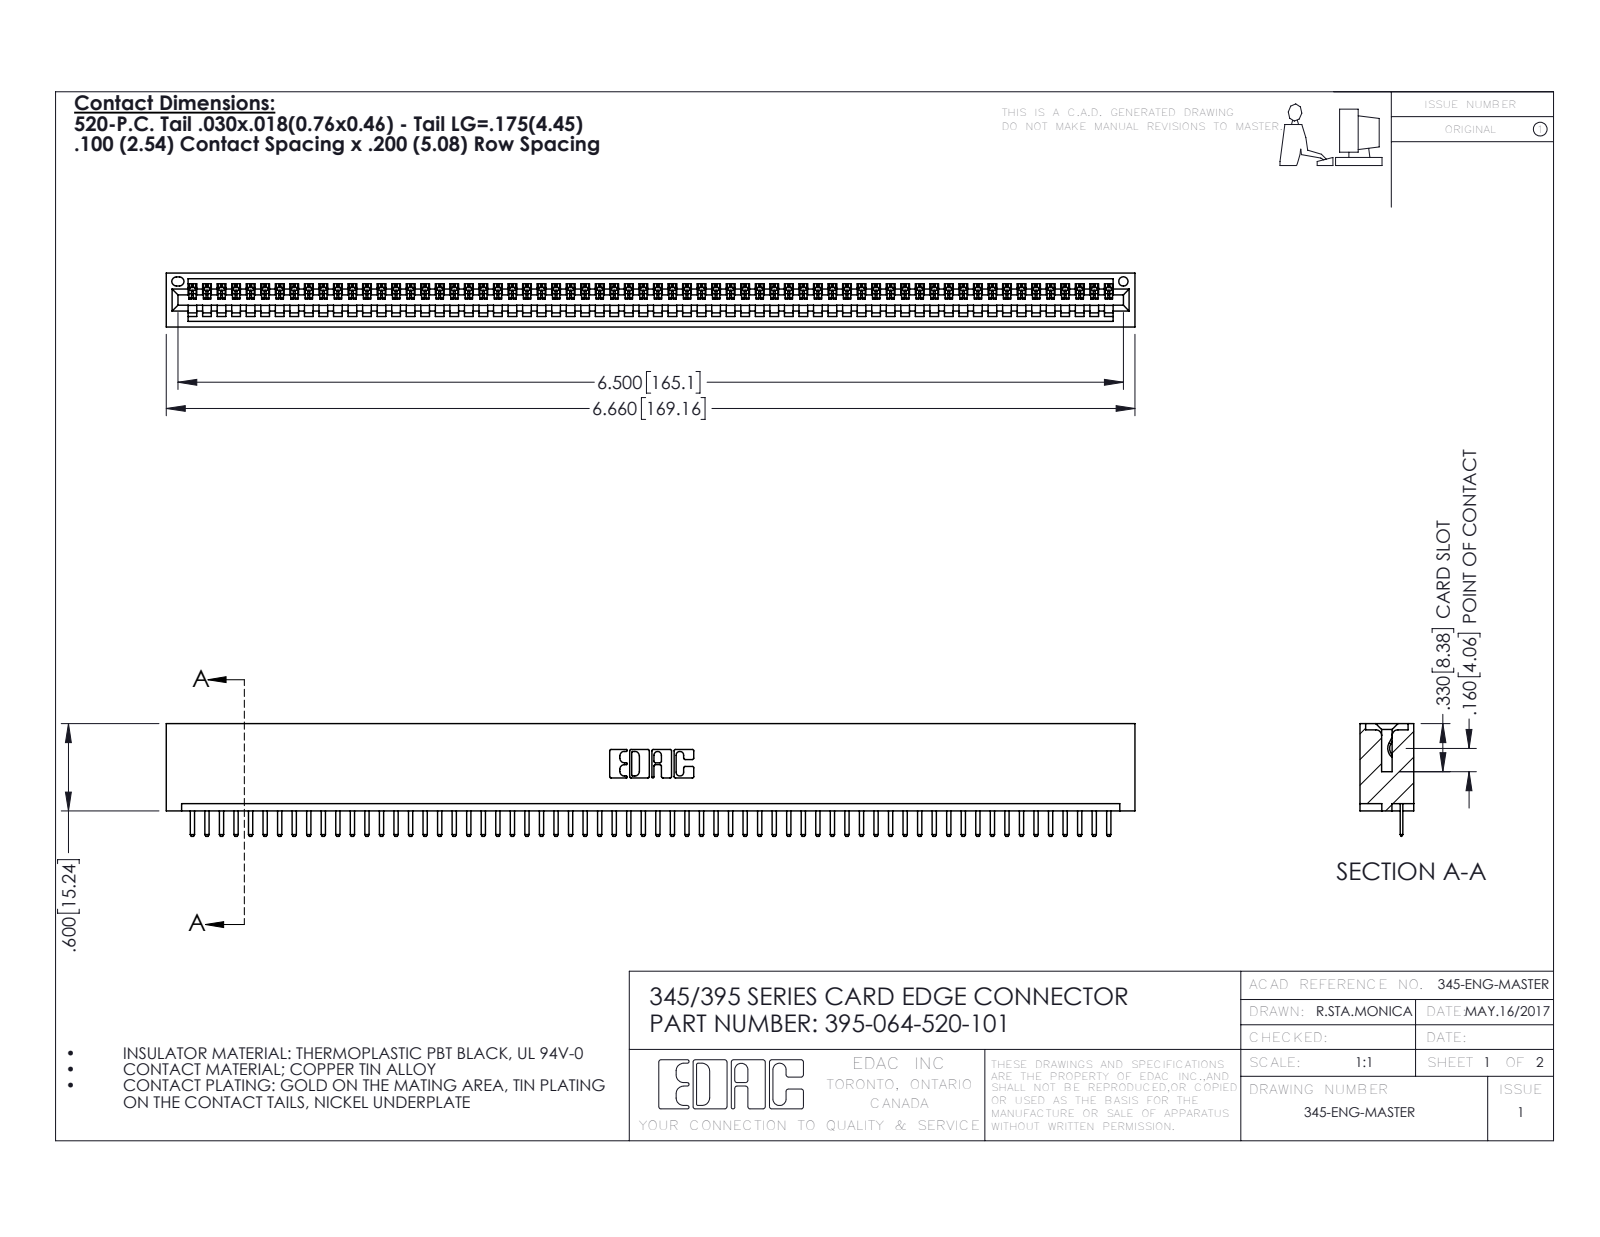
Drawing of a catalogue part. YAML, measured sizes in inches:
part_name: "345 Part_No Mounting Lugs; 345-292-001_345-293-120; 395-064-520-101"
step_written_by: "SolidWorks 2016 (CONFIG_CONTROL_DESIGN)"
units: inches
bodies: {solids: 65, faces: 4086, planar: 2764, cylindrical: 1322, other: 0}
overall_size: [6.66, 0.775, 0.37]
volume: 1.016
surface_area: 34.12
round_holes:
  - {diameter: 0.064, count: 1}
partial_cylinders:
  - {radius: 0.01, count: 130}
  - {radius: 0.006, count: 128}
  - {radius: 0.01, count: 22}
  - {radius: 0.007, count: 6}
  - {radius: 0.031, count: 6}
  - {radius: 0.026, count: 3}
  - {radius: 0.031, count: 2}
  - {radius: 0.04, count: 2}
face_to_face_distances: [0.298, 0.072, 0.37, 0.2, 0.098, 0.272, 0.025, 0.225, 0.072, 0.149]
